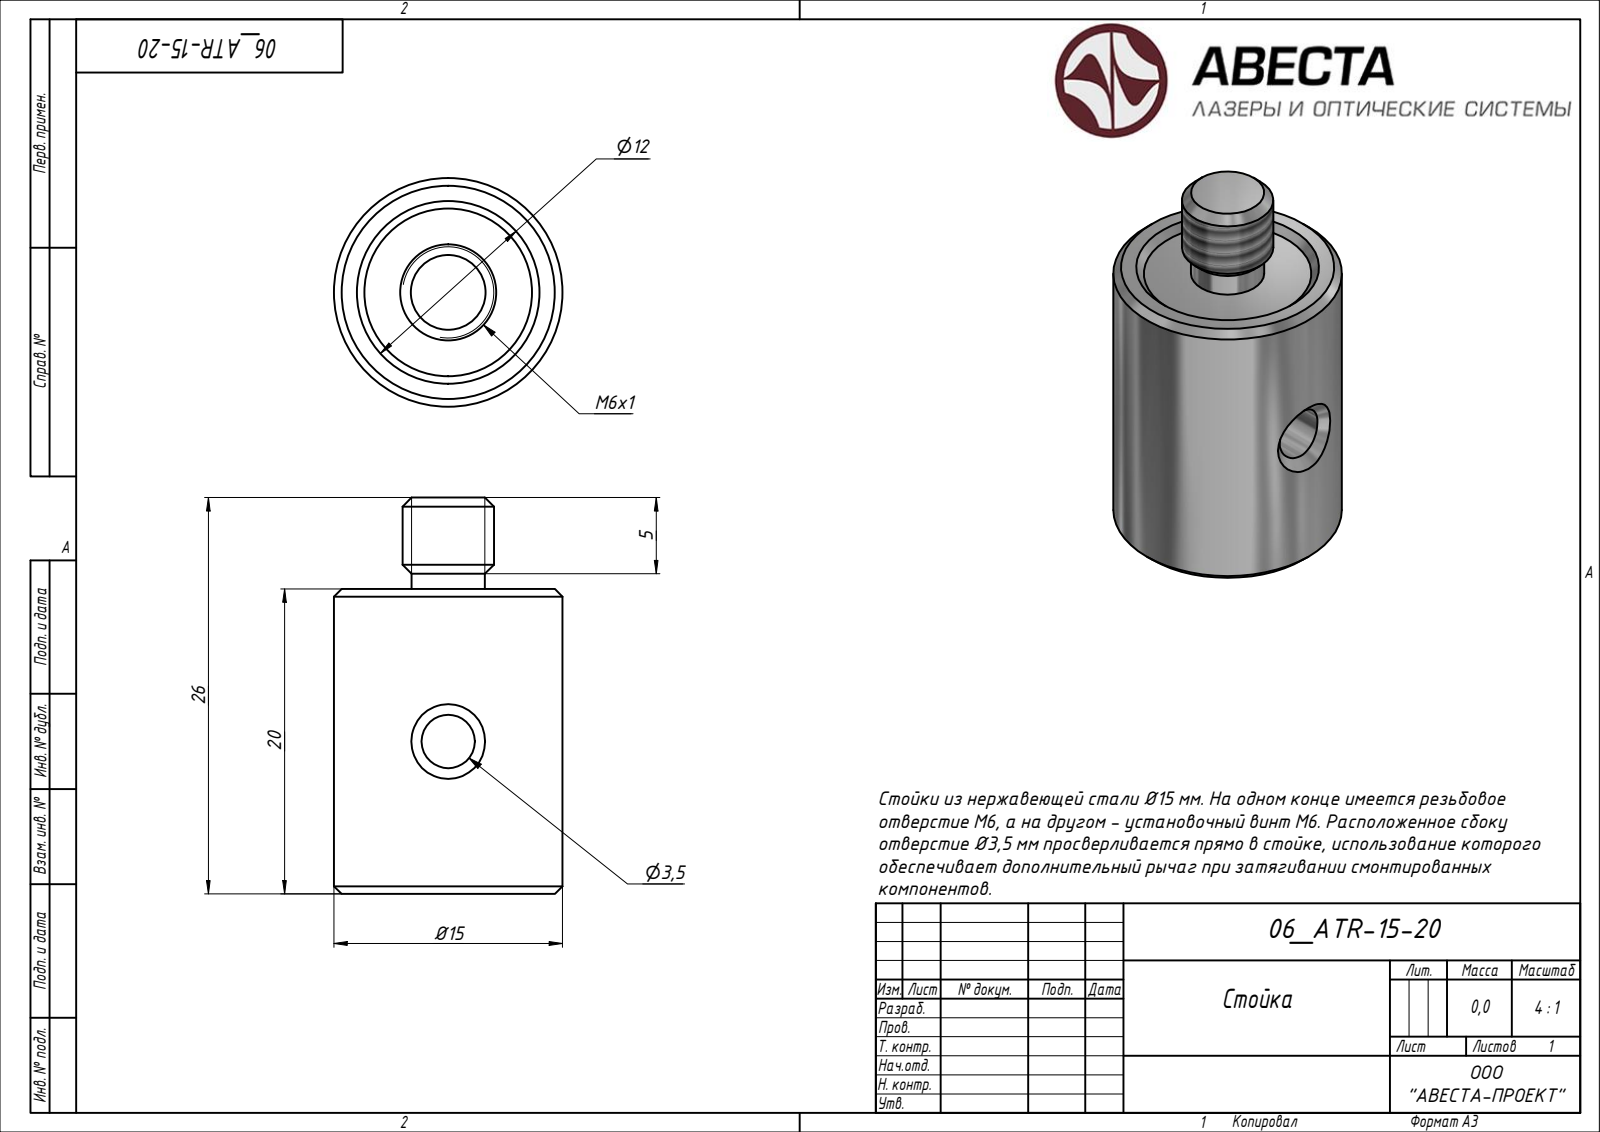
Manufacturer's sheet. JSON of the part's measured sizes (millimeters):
{"step_written_by": "ST-DEVELOPER v15 (AUTOMOTIVE_DESIGN)", "units": "millimeters", "bodies": {"solids": 7, "faces": 245, "planar": 35, "cylindrical": 0, "other": 210}, "overall_size": [183.87, 156, 15], "volume_mm3": 79913, "surface_area_mm2": 26459, "face_to_face_distances": [0.5, 20, 30, 50, 10, 80, 19.5, 49.5, 29.5, 39.5]}
